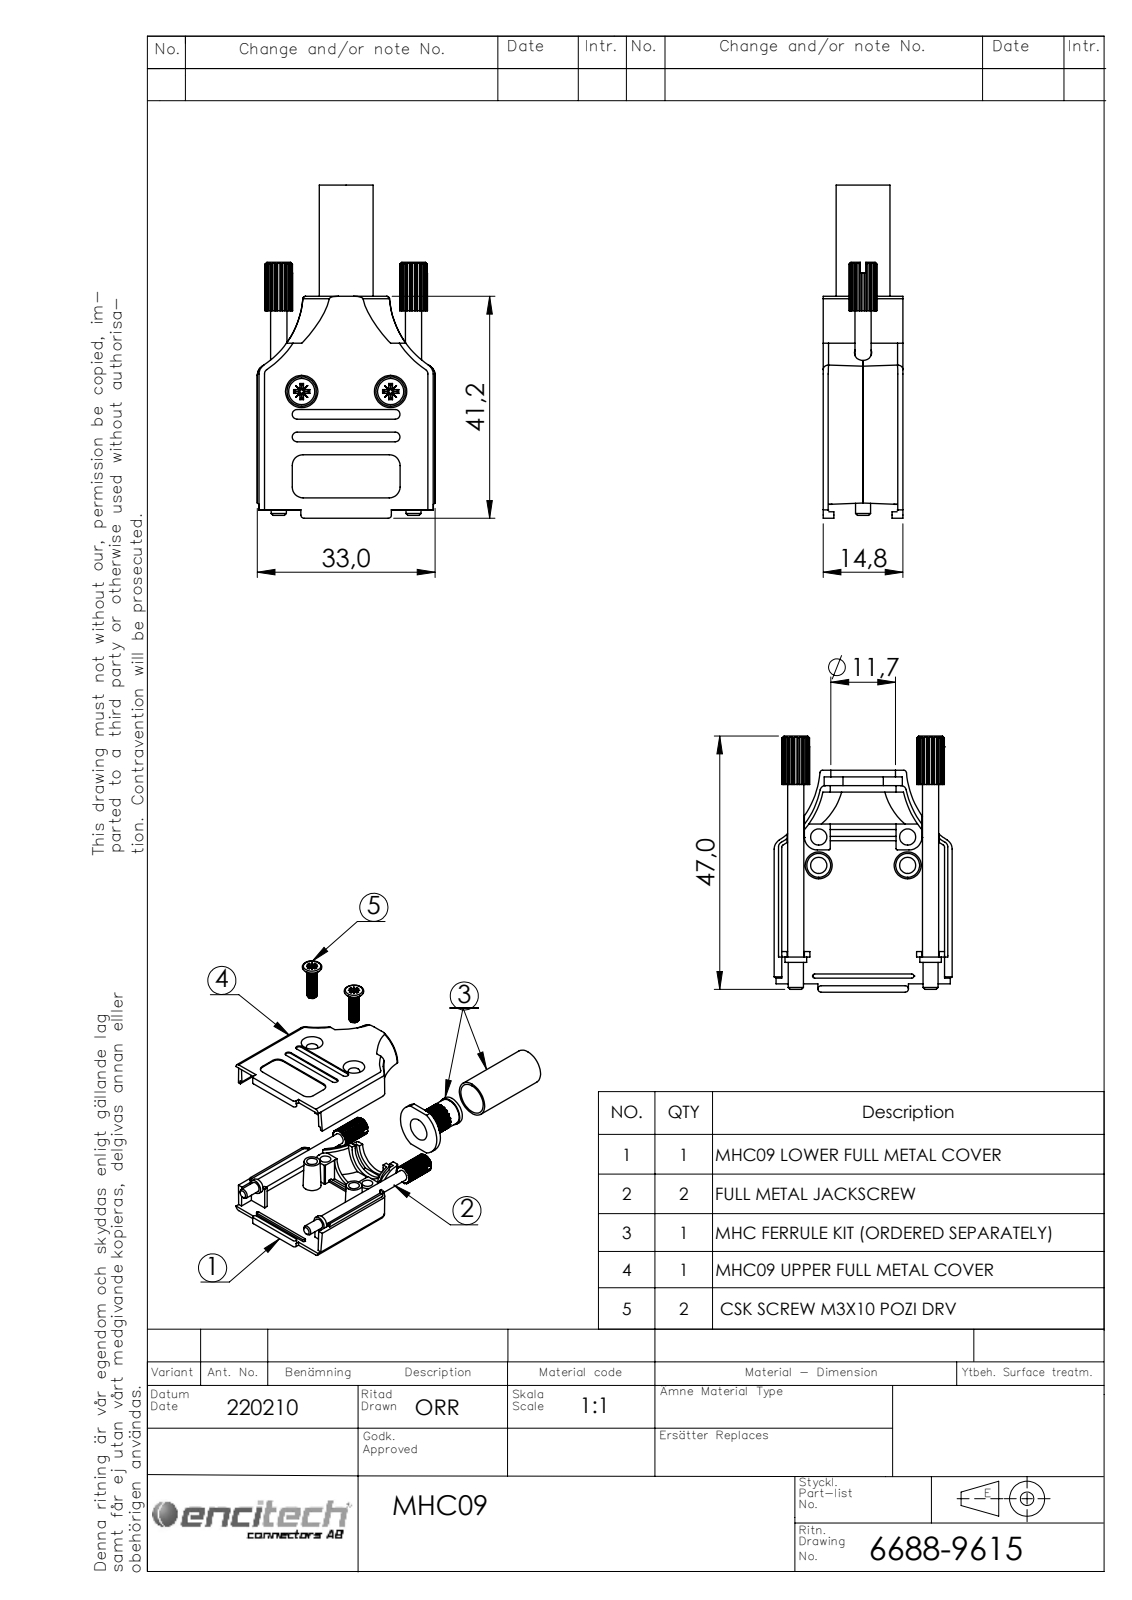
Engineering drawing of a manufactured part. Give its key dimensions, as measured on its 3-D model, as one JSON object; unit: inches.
{"part_name": "6805-0136-01; 6560-0135-01; 6826-0141-02; 6855-0117-03 (+3 more)", "step_written_by": "SolidWorks 2021 (AUTOMOTIVE_DESIGN)", "units": "inches", "bodies": {"solids": 8, "faces": 1687, "planar": 381, "cylindrical": 438, "other": 868}, "overall_size": [2.435, 1.299, 0.589], "volume_in3": 0.362, "surface_area_in2": 19.09, "round_holes": [[0.118, 4], [0.126, 4], [0.179, 2], [0.256, 1], [0.346, 1], [0.472, 1], [0.48, 1]], "round_bosses_or_shafts": [[0.205, 2], [0.157, 2], [0.118, 2], [0.114, 2], [0.11, 2], [0.394, 1], [0.315, 1], [0.295, 1]], "partial_cylinders_radius": [[0.004, 12], [0.039, 10], [0.646, 10], [0.01, 5], [0.035, 4], [0.079, 4], [0.016, 2], [0.02, 2]], "face_to_face_distances": [0.041, 0.541, 0.5, 0.583, 0.53, 0.571, 0.03, 1.189, 1.298, 0.28], "hole_center_spacings": [0.207, 0.492, 0.65, 0.682, 0.984]}
